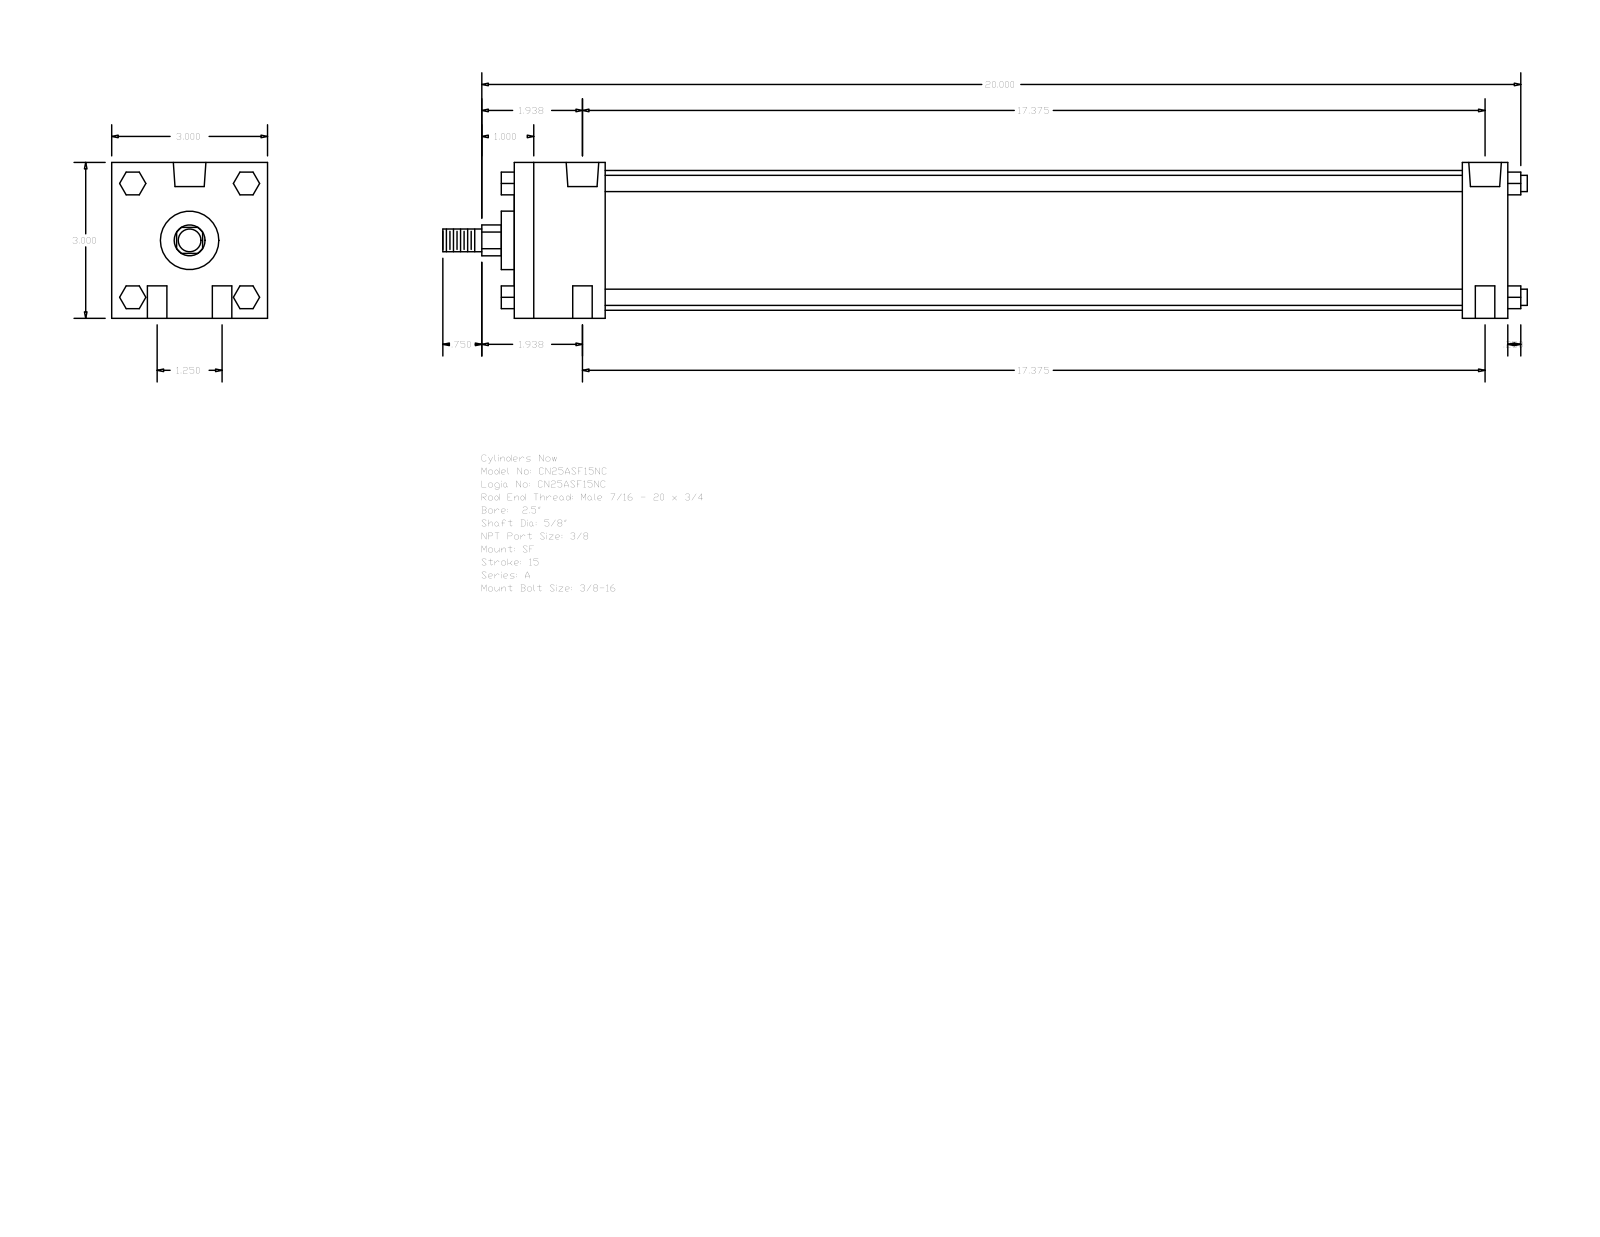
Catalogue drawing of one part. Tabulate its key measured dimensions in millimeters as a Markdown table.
| quantity | value |
| --- | --- |
| part name | A_SF__0250_0.625 |
| STEP written by | GSSL Pune (CONFIG_CONTROL_DESIGN) |
| units | millimeters |
| bodies | 0 solids, 124 faces (94 planar, 30 cylindrical, 0 other) |
| overall size | 530.23 × 76.2 × 76.2 |
| round holes (diameter × count) | 9.53 × 4, 5.56 × 2, 15.93 × 2 |
| round bosses / shafts (diameter × count) | 7.94 × 4, 68.33 × 1, 28.57 × 1, 15.88 × 1, 11.11 × 1 |
| partial cylindrical surfaces (radius × count) | 7.54 × 1 |
| main face-to-face distances | 76.2, 485.77, 44.45, 463.55, 22.22, 419.1, 441.32, 6.35, 492.12, 50.8 |
| hole center spacings | 15.88, 441.62, 441.33, 31.76, 442.47, 446.09 |
